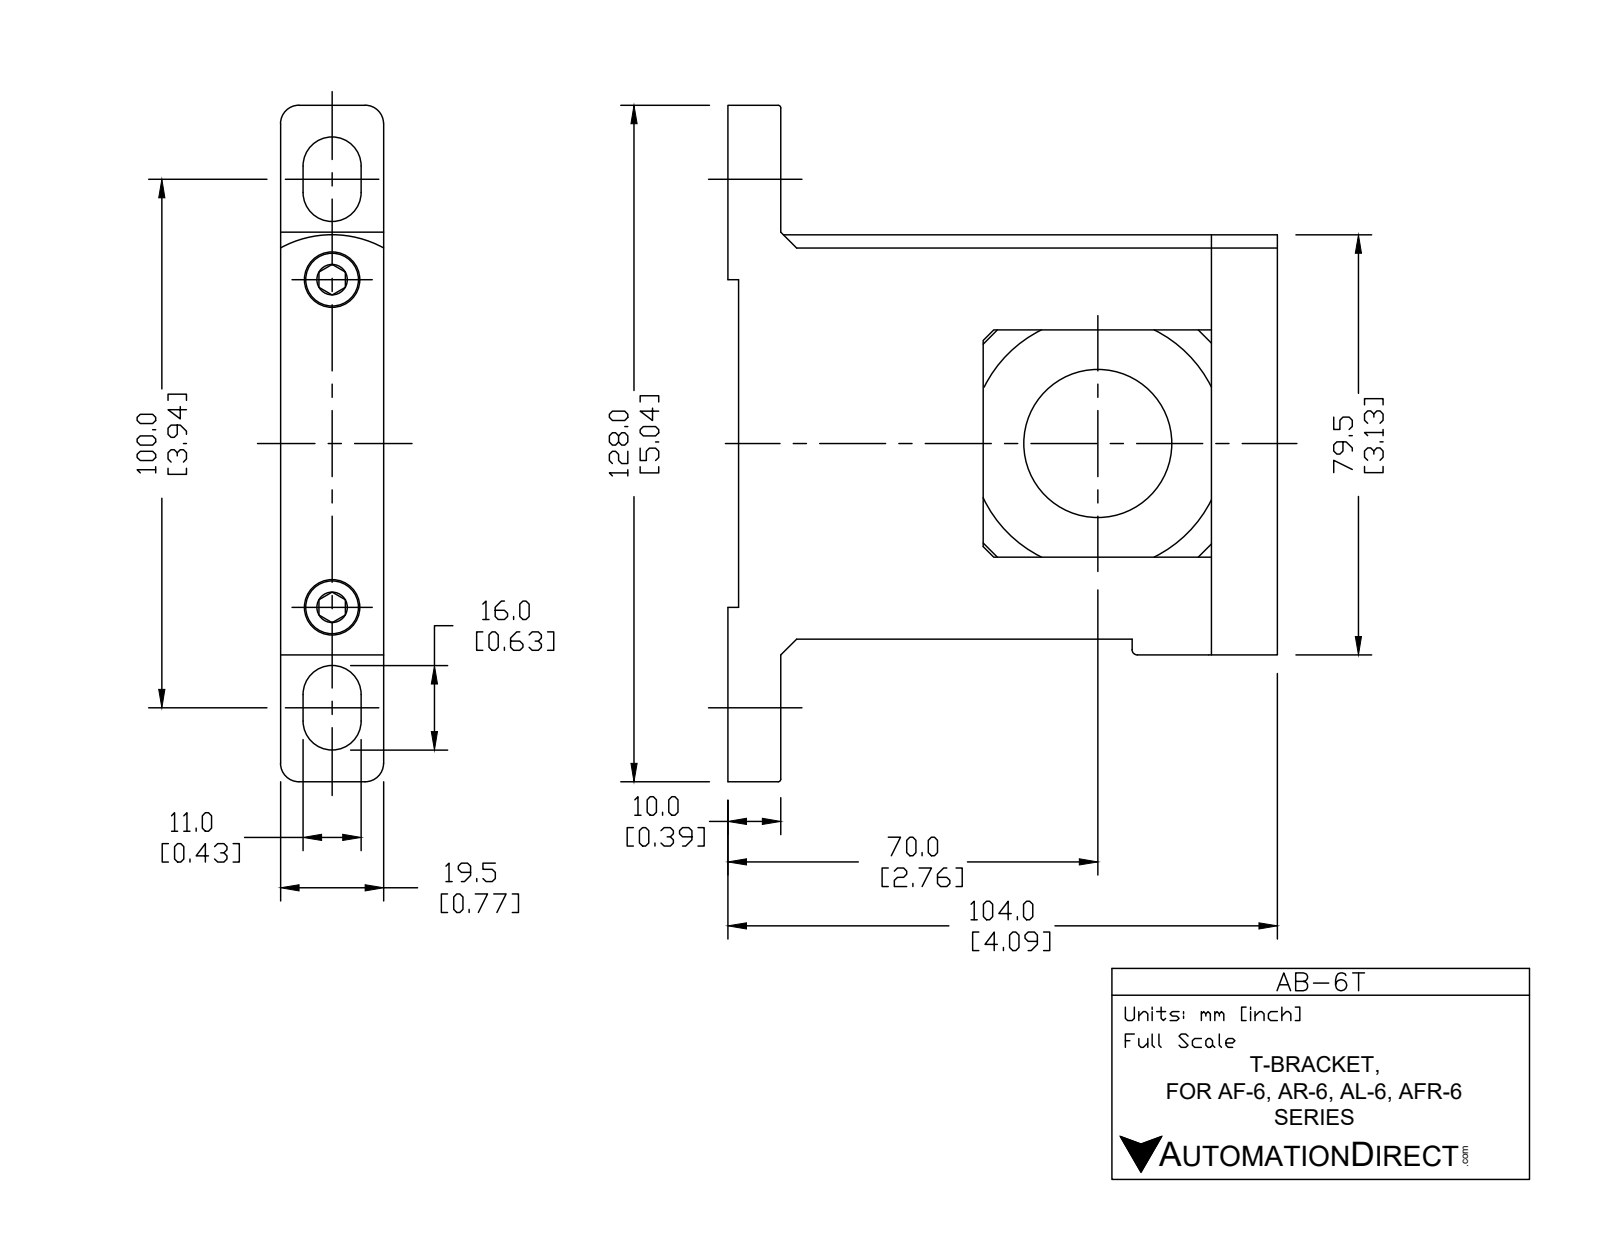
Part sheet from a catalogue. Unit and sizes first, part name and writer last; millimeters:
Units: millimetres
Overall size (bounding box): 128 × 104 × 19.5
Round holes (diameter × count): ⌀6.5 ×2, ⌀10.53 ×2, ⌀28 ×1
Round bosses / shafts (diameter × count): ⌀9.75 ×2, ⌀4 ×2
Partial cylindrical surfaces — rounded edges, fillets, slot ends (radius × count): R5.5 ×4, R1.5 ×1, R20.26 ×1
Main face-to-face distances: 19.5, 3, 46, 102.25, 8.94, 10.56, 12.5, 3.75, 15.75, 5.19
Hole centre spacings: 62
Volume: 122 405 mm³ · Surface area: 32 406 mm²
Bodies: 3 solids, 110 faces (74 planar, 24 cylindrical, 12 other)
Part name (STEP PRODUCT): AB-6T
STEP written by: SolidWorks 2015 (CONFIG_CONTROL_DESIGN)
